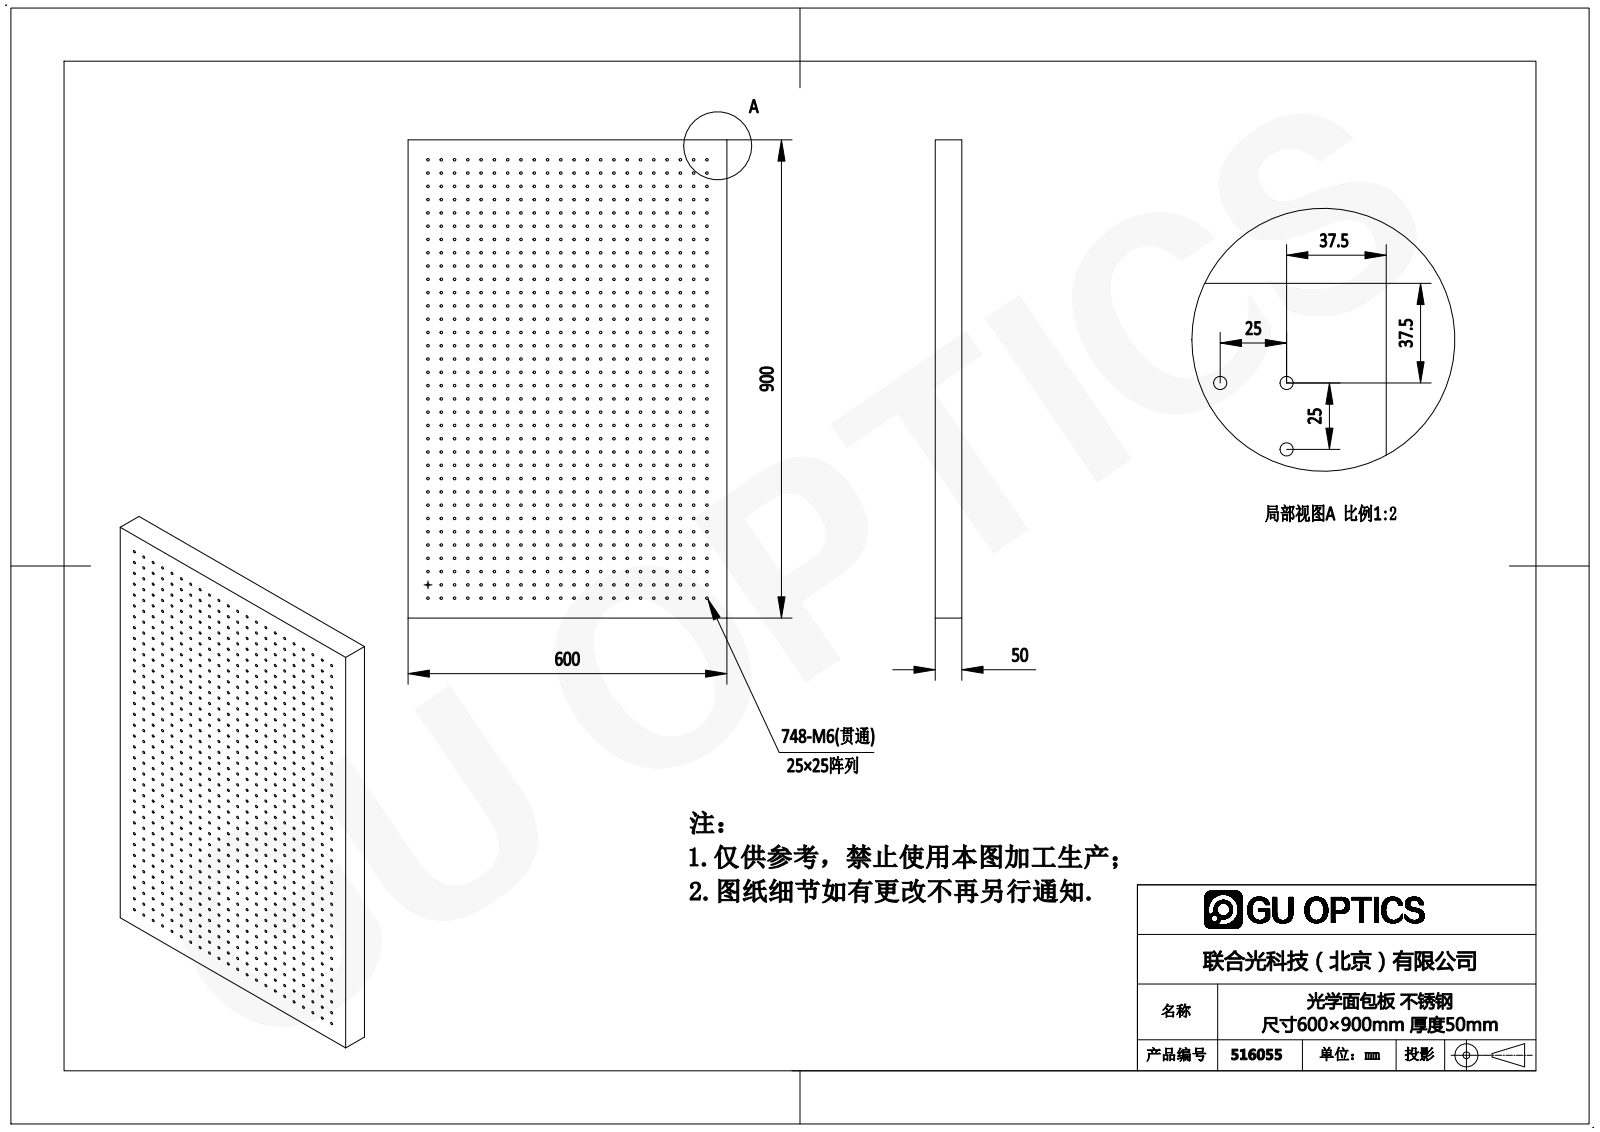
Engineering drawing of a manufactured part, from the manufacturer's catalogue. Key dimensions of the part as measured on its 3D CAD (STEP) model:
Part name (STEP PRODUCT): 516055
STEP written by: SolidWorks 2016 (AUTOMOTIVE_DESIGN)
Units: millimetres
Bodies: 1 solid, 1502 faces (6 planar, 1496 cylindrical, 0 other)
Overall size (bounding box): 900 × 600 × 50
Volume: 26 270 000 mm³ · Surface area: 1 788 000 mm²
Round holes (diameter × count): ⌀5 ×748
Main face-to-face distances: 50, 600, 900
Hole centre spacings: 25, 50, 75, 100, 125, 150, 175, 200
